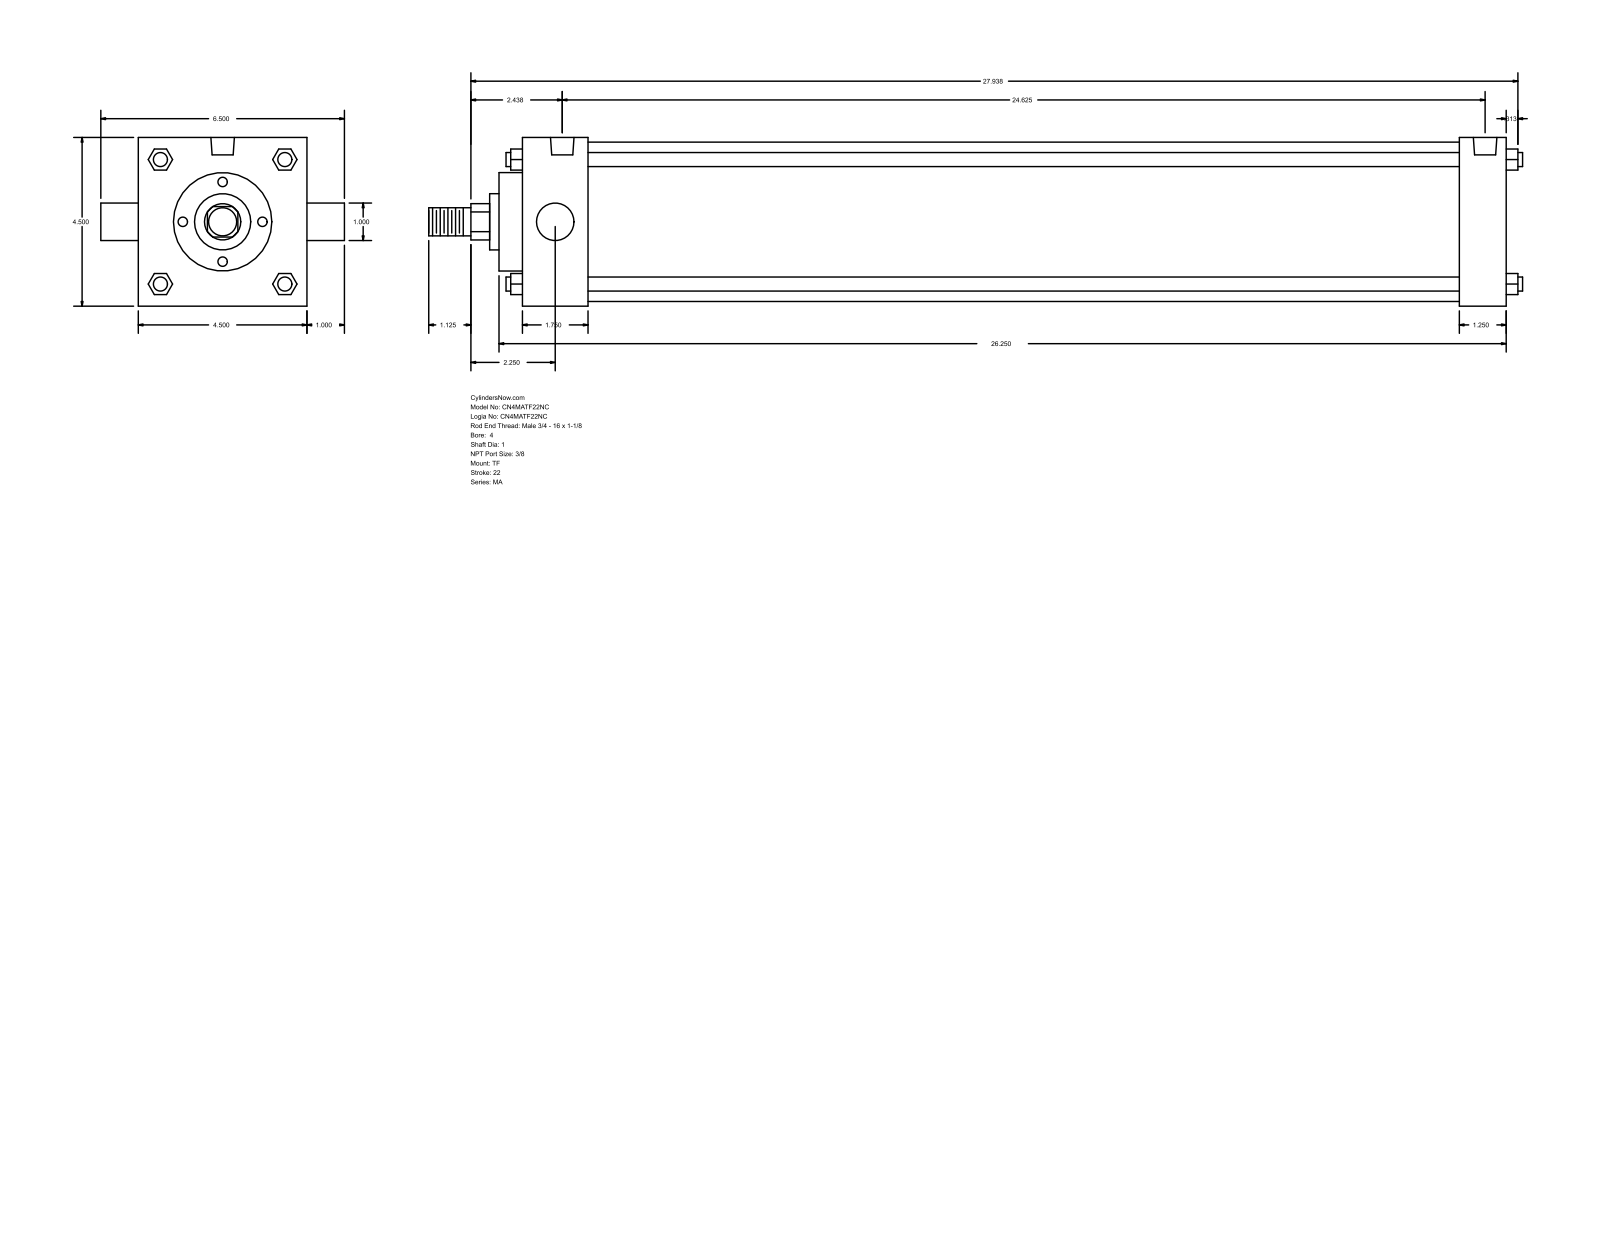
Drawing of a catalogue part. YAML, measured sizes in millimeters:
part_name: "MA_TF__0400_1"
step_written_by: "GSSL Pune (CONFIG_CONTROL_DESIGN)"
units: millimeters
bodies: {solids: 0, faces: 122, planar: 93, cylindrical: 29, other: 0}
overall_size: [741.36, 165.1, 114.3]
round_holes:
  - {diameter: 11.11, count: 3}
  - {diameter: 15.93, count: 2}
round_bosses_or_shafts:
  - {diameter: 9.53, count: 4}
  - {diameter: 25.4, count: 2}
  - {diameter: 107.95, count: 1}
  - {diameter: 66.67, count: 1}
  - {diameter: 38.1, count: 1}
  - {diameter: 19.05, count: 1}
partial_cylinders:
  - {radius: 12.29, count: 1}
face_to_face_distances: [114.3, 666.75, 635, 31.75, 44.46, 590.54, 622.29, 682.62, 15.87, 60.33]
hole_center_spacings: [4.76, 4.77, 615.95, 620.71, 620.72, 625.48]
